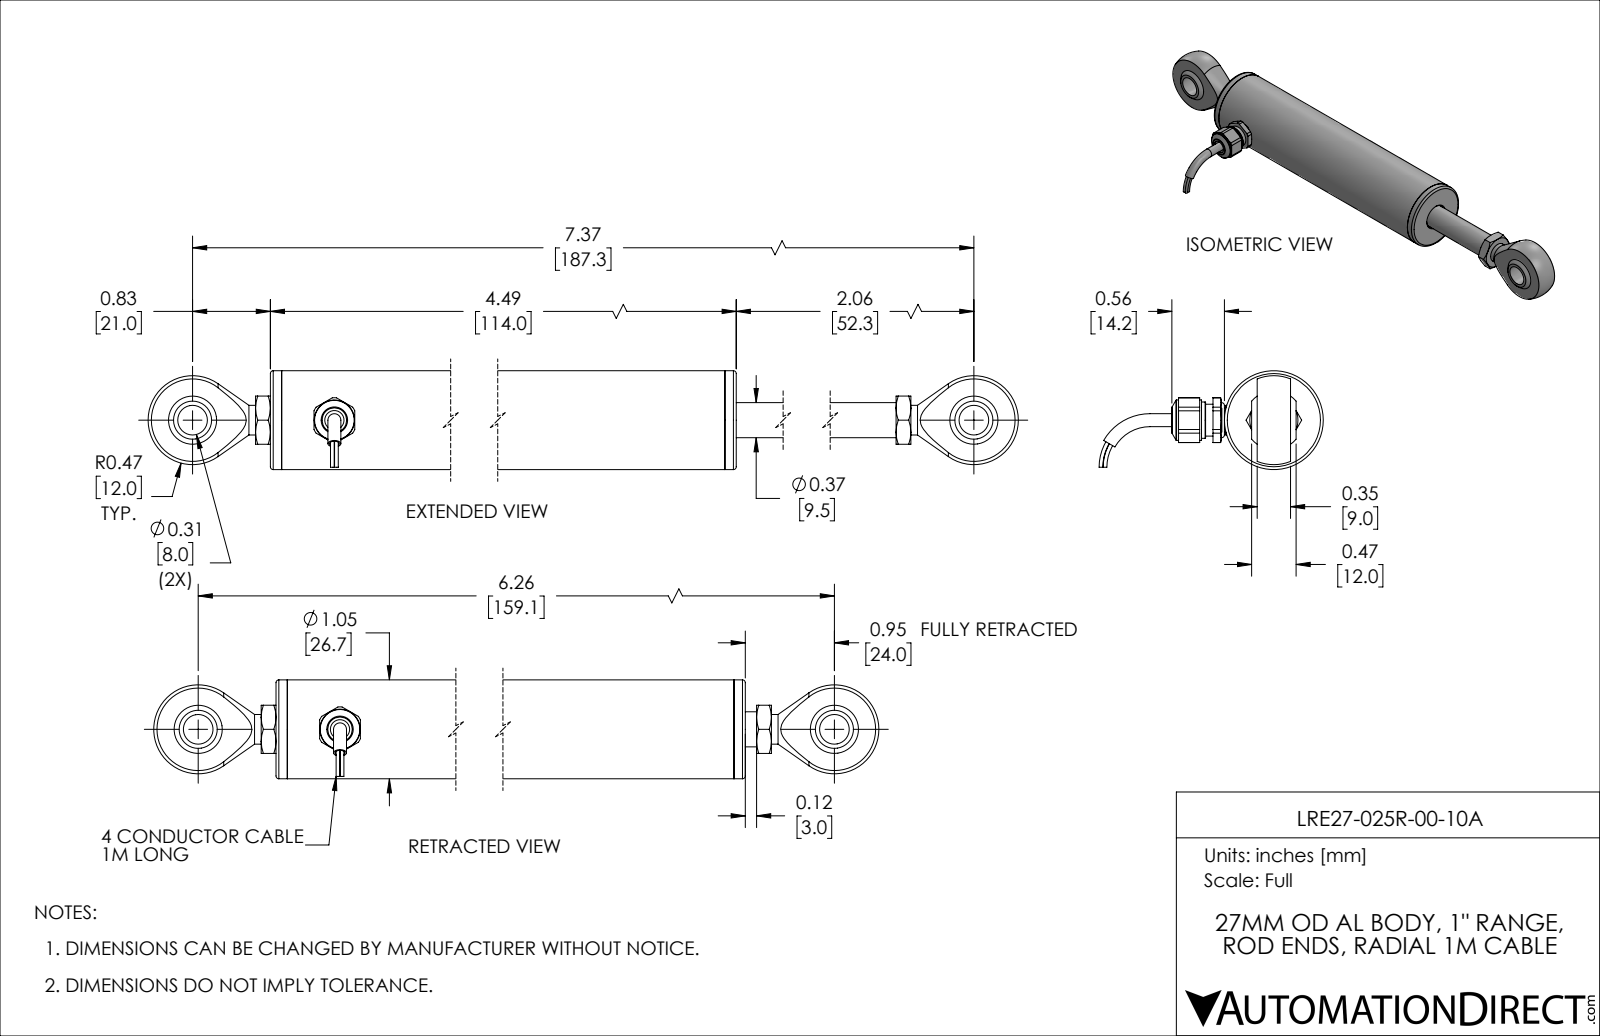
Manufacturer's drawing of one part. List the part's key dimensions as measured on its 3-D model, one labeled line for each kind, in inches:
Part name (STEP PRODUCT): LRE27-025R-00-10A
STEP written by: SolidWorks 2019 (AUTOMOTIVE_DESIGN)
Units: inches
Bodies: 17 solids, 227 faces (82 planar, 55 cylindrical, 90 other)
Overall size (bounding box): 7.208 × 2.382 × 1.05
Volume: 2.856 in³ · Surface area: 56.99 in²
Round holes (diameter × count): ⌀0.268 ×2, ⌀0.106 ×1, ⌀0.138 ×1, ⌀0.201 ×1, ⌀0.205 ×1, ⌀0.274 ×1, ⌀0.36 ×1, ⌀0.375 ×1, ⌀0.386 ×1, ⌀0.499 ×1, ⌀0.825 ×1, ⌀0.851 ×1
Round bosses / shafts (diameter × count): ⌀0.315 ×4, ⌀0.039 ×4, ⌀1.05 ×1, ⌀0.848 ×1, ⌀0.5 ×1, ⌀0.429 ×1, ⌀0.386 ×1, ⌀0.373 ×1
Partial cylindrical surfaces — rounded edges, fillets, slot ends (radius × count): R0.238 ×1
Main face-to-face distances: 0.12, 4.37, 0.354, 4.49, 4.25, 0.4, 0.28, 3.97, 4.09, 0.157
